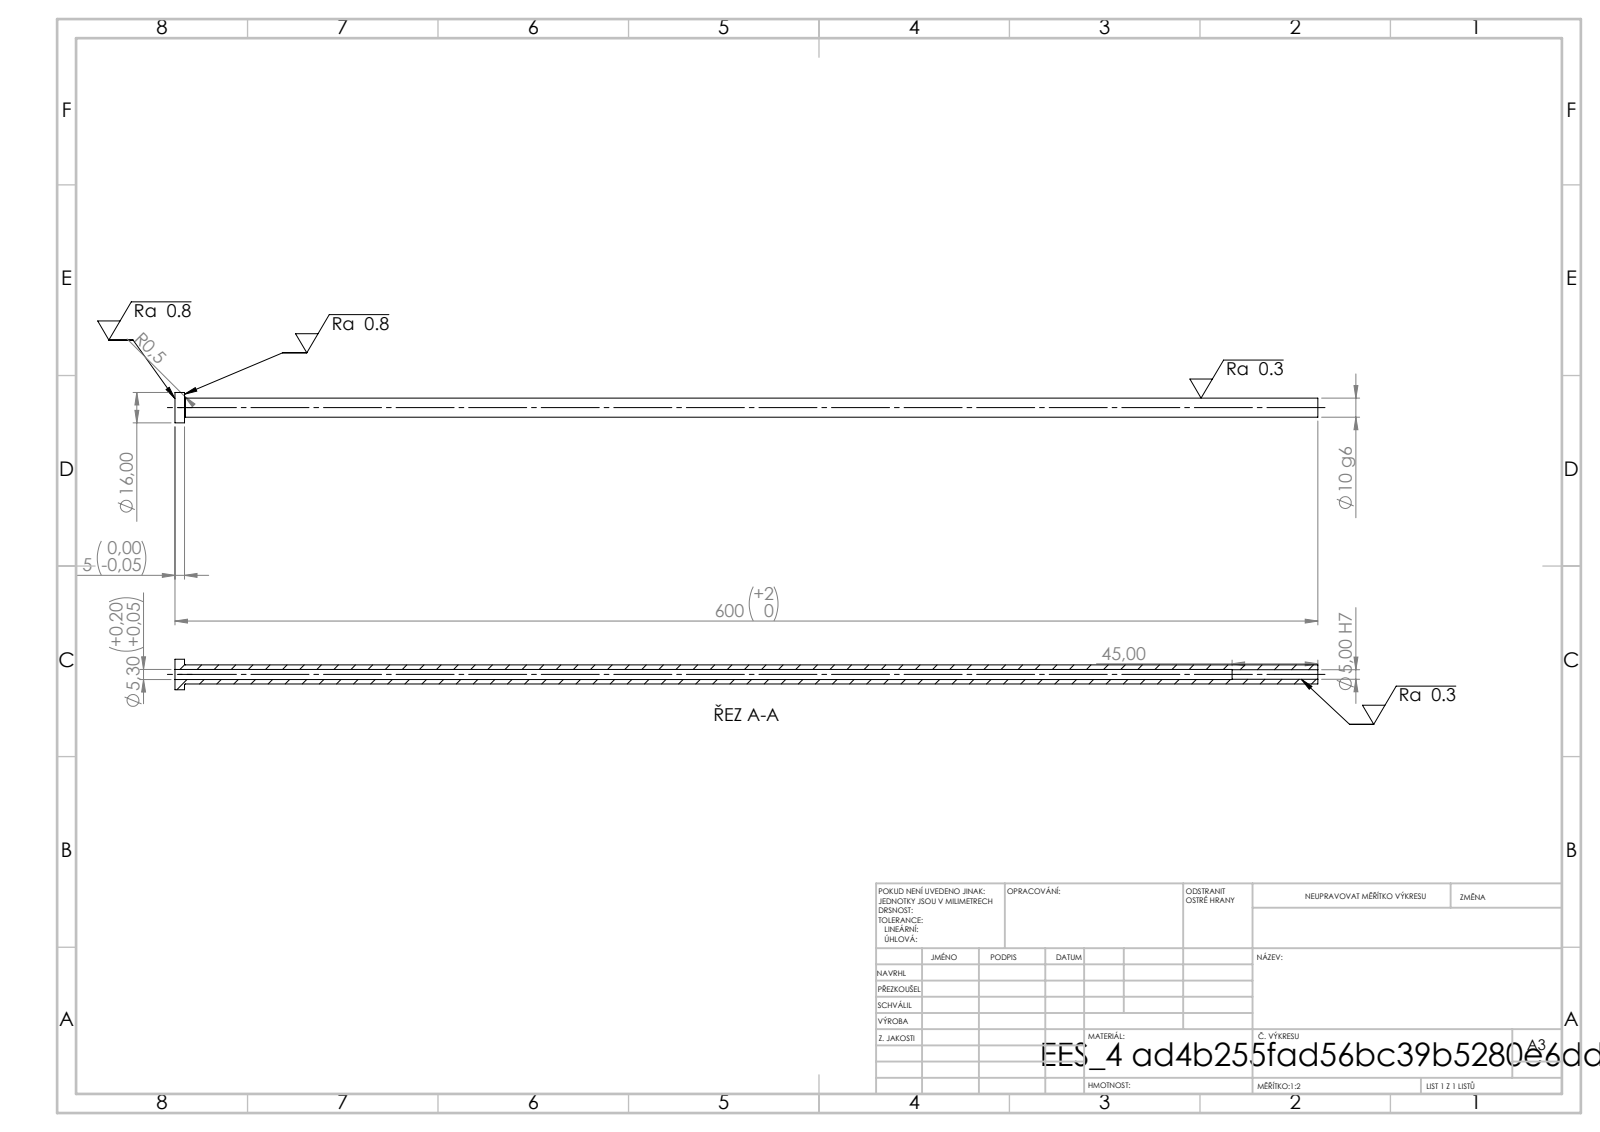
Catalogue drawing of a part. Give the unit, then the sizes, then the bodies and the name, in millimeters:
Units: millimetres
Overall size (bounding box): 600 × 16 × 16
Round holes (diameter × count): ⌀5 ×1, ⌀5.3 ×1
Round bosses / shafts (diameter × count): ⌀16 ×1, ⌀10 ×1
Main face-to-face distances: 5, 600, 595, 555, 550, 45
Volume: 34 610 mm³ · Surface area: 29 248 mm²
Bodies: 1 solid, 14 faces (4 planar, 8 cylindrical, 2 other)
STEP written by: SolidWorks 2019 (CONFIG_CONTROL_DESIGN)
